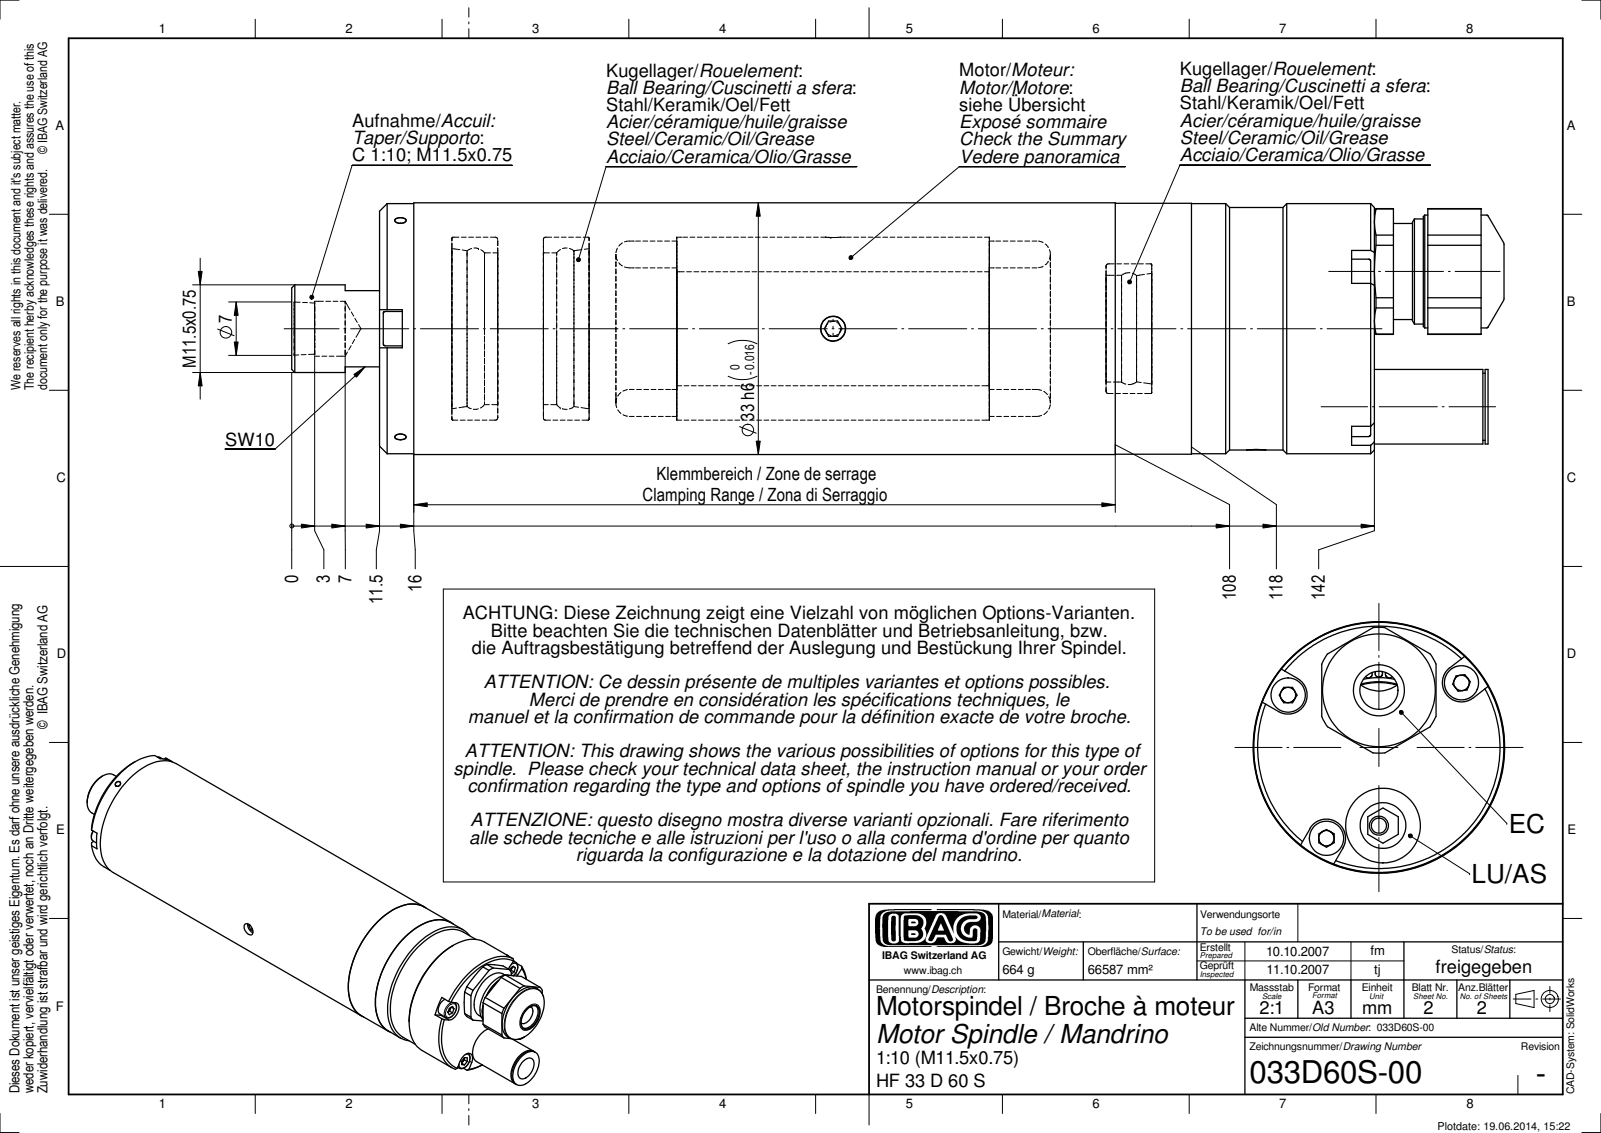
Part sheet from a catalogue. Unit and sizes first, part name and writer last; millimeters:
Units: millimetres
Overall size (bounding box): 159 × 33 × 33
Round holes (diameter × count): ⌀3.3 ×1, ⌀5 ×1, ⌀6 ×1, ⌀6.7 ×1, ⌀7.2 ×1, ⌀11.9 ×1
Round bosses / shafts (diameter × count): ⌀4.5 ×6, ⌀33 ×1, ⌀32.9 ×1, ⌀32.8 ×1, ⌀31.8 ×1, ⌀14.8 ×1, ⌀13.79 ×1, ⌀12.59 ×1
Partial cylindrical surfaces — rounded edges, fillets, slot ends (radius × count): R2.5 ×6, R8.25 ×1
Main face-to-face distances: 130.5, 106.5, 24, 10, 4.5, 96.5, 34, 92, 102, 126
Hole centre spacings: 7.5, 10.25, 17.75
Bodies: 0 solids, 245 faces (113 planar, 77 cylindrical, 55 other)
Part name (STEP PRODUCT): 033D60S-00
STEP written by: SolidWorks 2014 (CONFIG_CONTROL_DESIGN)
